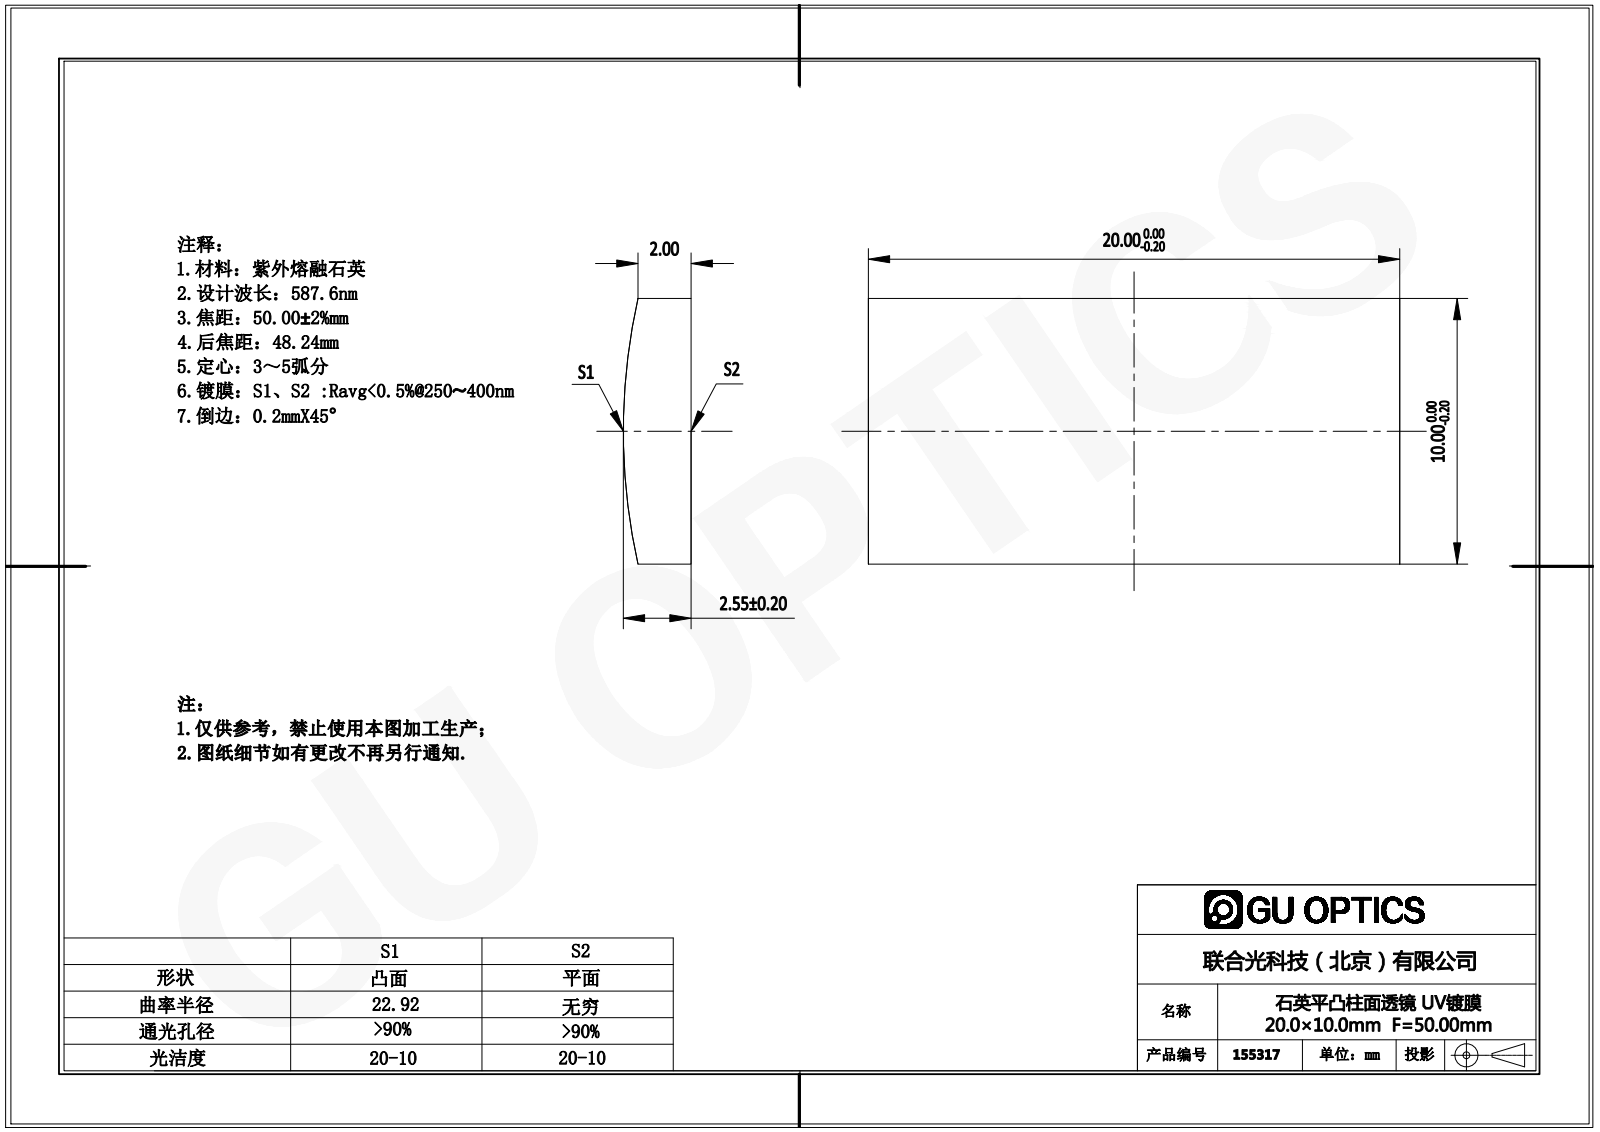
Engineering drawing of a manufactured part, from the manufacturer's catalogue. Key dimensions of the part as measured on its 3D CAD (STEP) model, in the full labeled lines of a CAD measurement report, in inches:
Part name (STEP PRODUCT): 155283
STEP written by: SolidWorks 2016 (AUTOMOTIVE_DESIGN)
Units: inches
Bodies: 1 solid, 6 faces (5 planar, 1 cylindrical, 0 other)
Overall size (bounding box): 0.787 × 0.394 × 0.1
Volume: 0.029 in³ · Surface area: 0.82 in²
Partial cylindrical surfaces — rounded edges, fillets, slot ends (radius × count): R0.902 ×1
Main face-to-face distances: 0.394, 0.787
